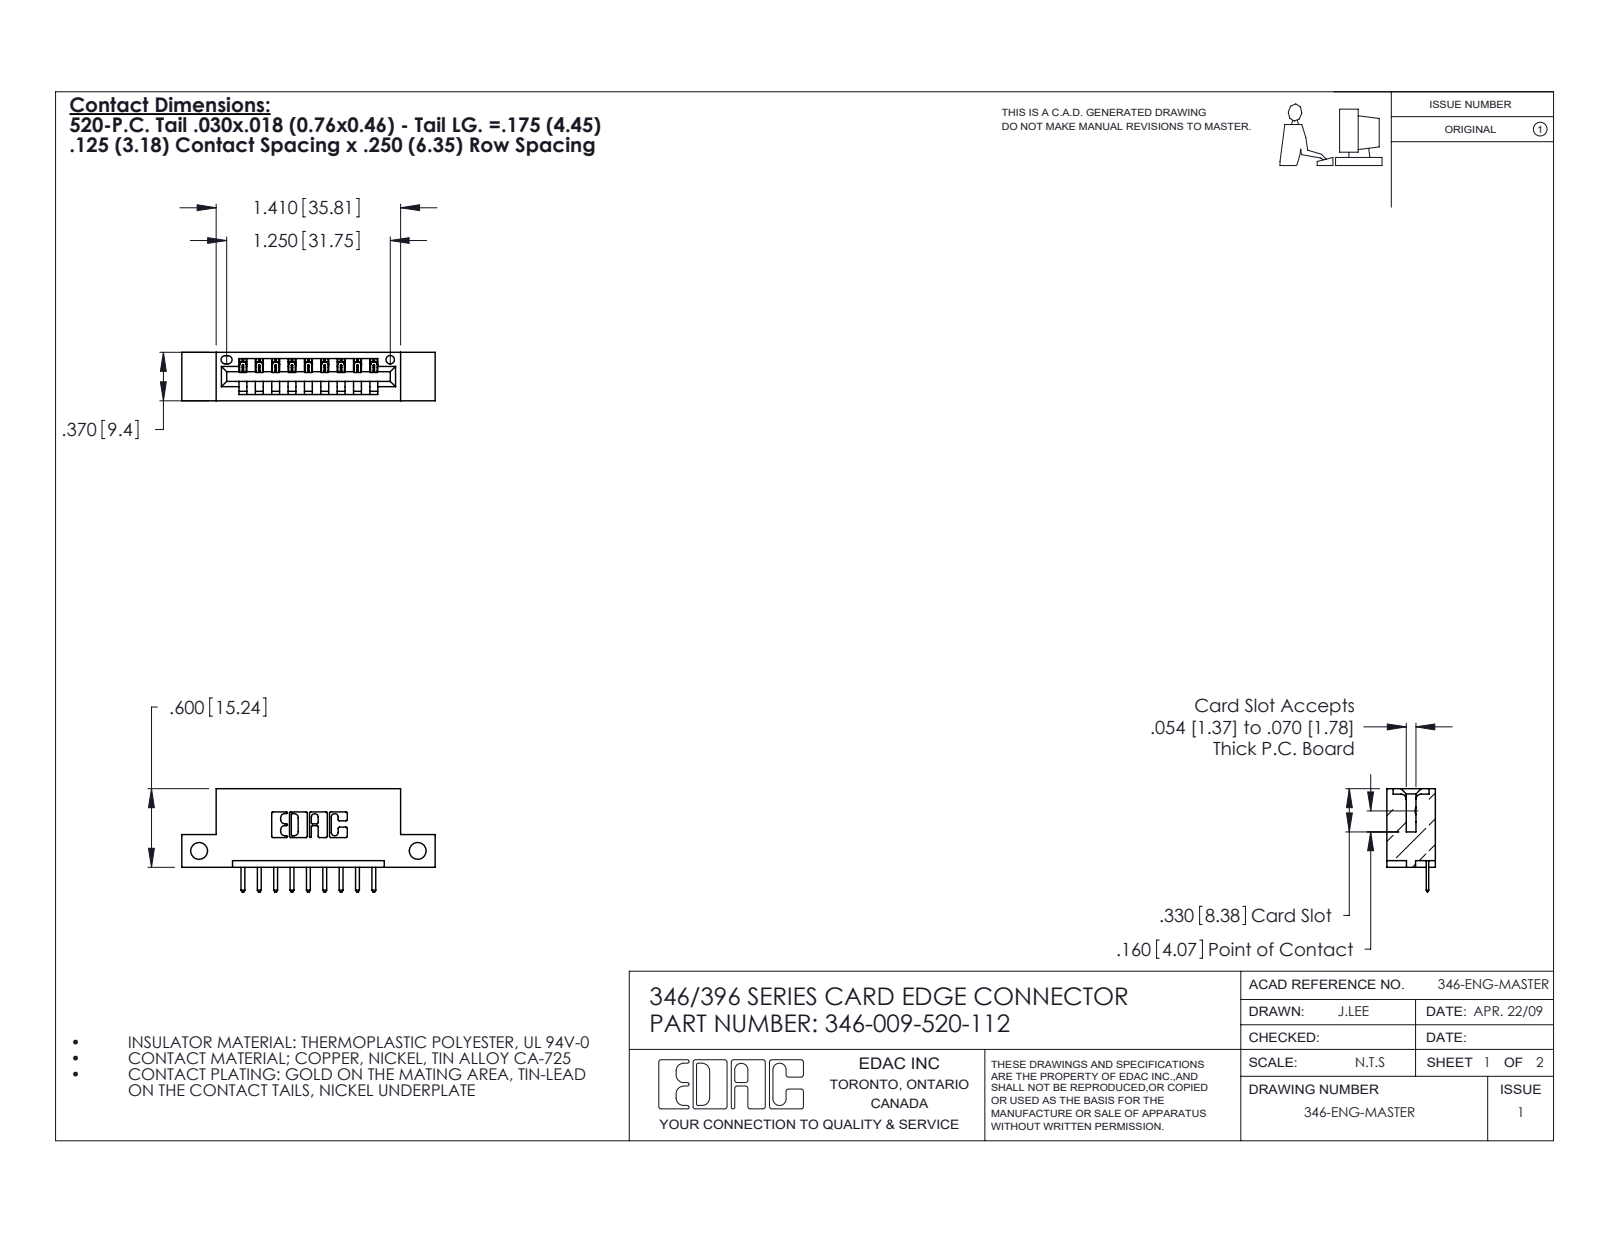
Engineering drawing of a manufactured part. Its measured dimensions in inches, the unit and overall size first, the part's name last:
Units: inches
Overall size (bounding box): 1.935 × 0.788 × 0.37
Round holes (diameter × count): ⌀0.128 ×2, ⌀0.064 ×1
Partial cylindrical surfaces — rounded edges, fillets, slot ends (radius × count): R0.01 ×22, R0.01 ×20, R0.006 ×18, R0.007 ×6, R0.031 ×6, R0.026 ×3, R0.031 ×2, R0.04 ×2
Main face-to-face distances: 0.25, 0.37, 0.048, 0.322, 0.148, 0.222, 0.1, 0.174, 0.125, 0.5
Hole centre spacings: 1.67
Volume: 0.266 in³ · Surface area: 7.543 in²
Bodies: 10 solids, 680 faces (454 planar, 226 cylindrical, 0 other)
Part name (STEP PRODUCT): 346-009-520-112; 345-292-001_345-293-120; 346 Part_Flush Mounting Lugs - Side Mount
STEP written by: SolidWorks 2020 (CONFIG_CONTROL_DESIGN)
